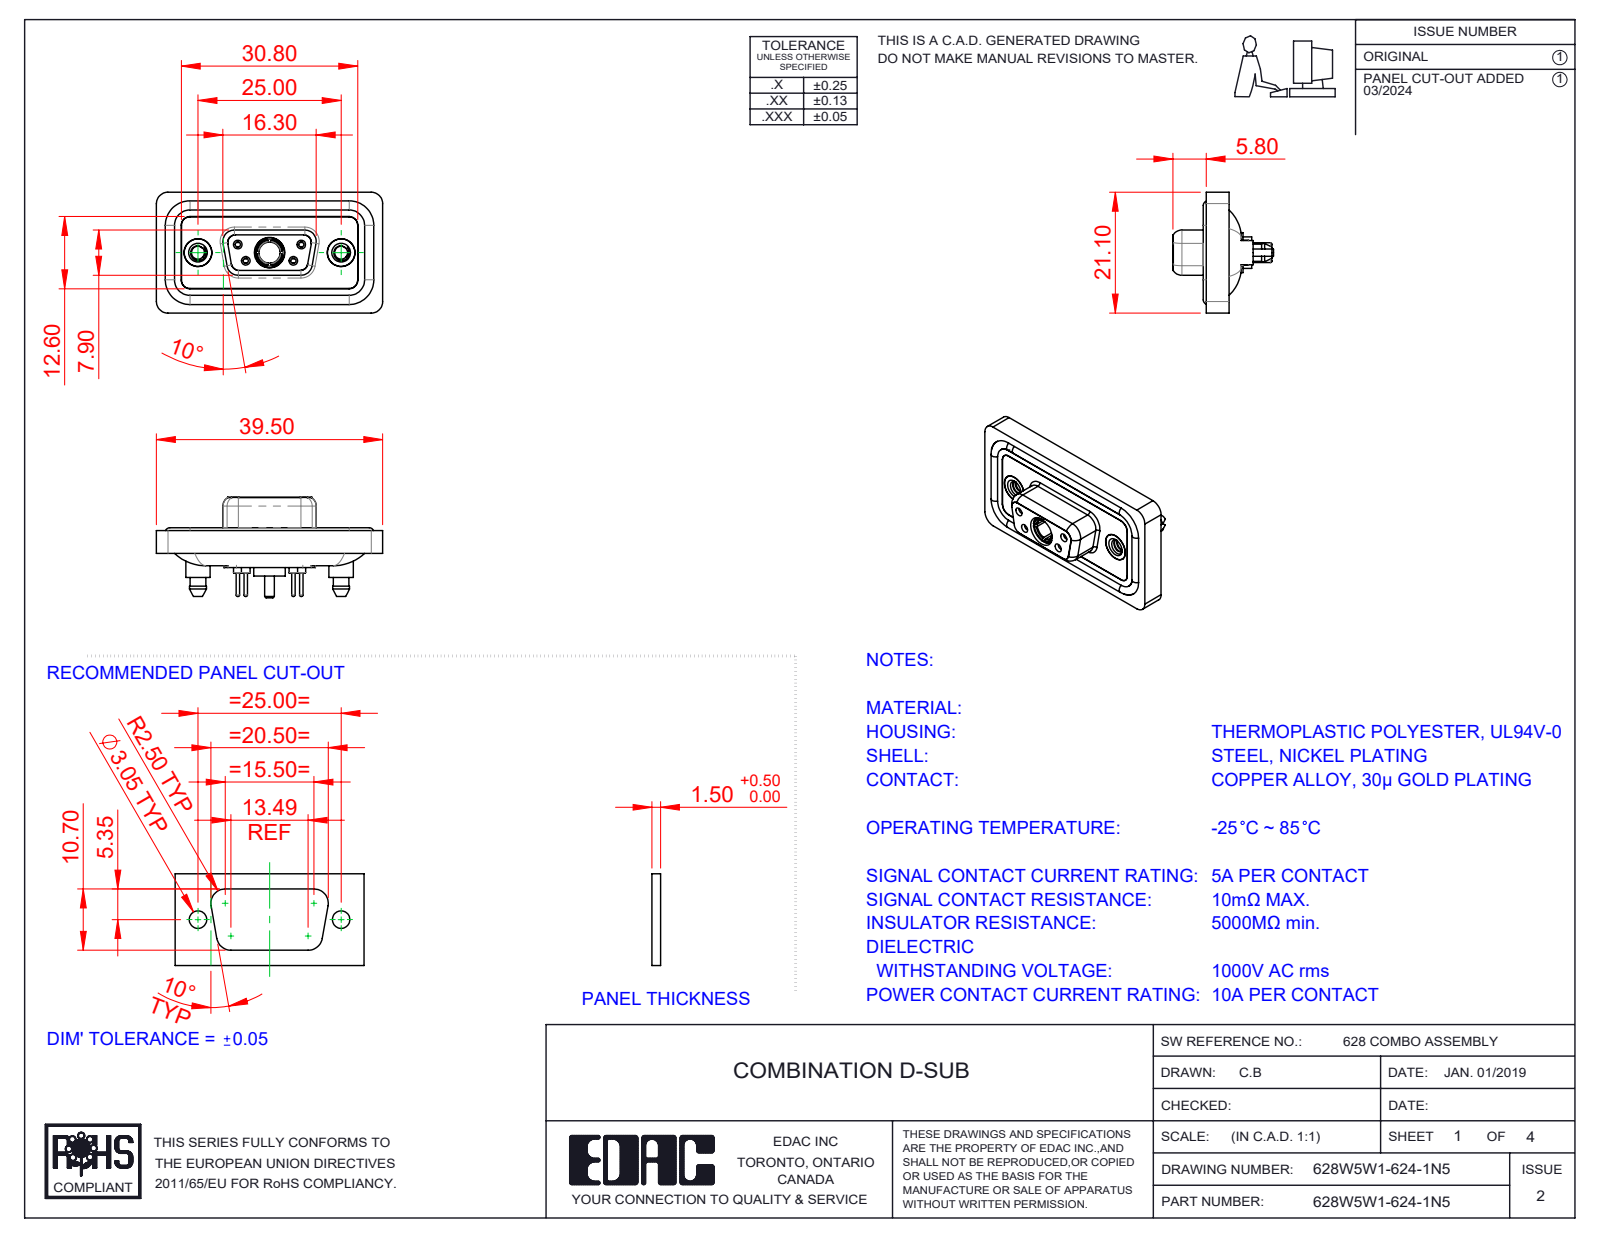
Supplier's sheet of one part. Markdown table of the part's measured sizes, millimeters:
| quantity | value |
| --- | --- |
| part name | 628Combo Threaded Boardlock_5; 628Combo Shell Front_09 Contacts; 628W5W1-624-1N5; 628Combo Shell Rear_09 Contacts (+5 more) |
| STEP written by | SolidWorks 2023 (CONFIG_CONTROL_DESIGN) |
| units | millimeters |
| bodies | 13 solids, 730 faces (210 planar, 319 cylindrical, 201 other) |
| overall size | 39.5 × 21.1 × 17.55 |
| volume | 4 886 mm³ |
| surface area | 7 956 mm² |
| round holes (diameter × count) | 0.9 × 4, 1.1 × 4, 1.5 × 4, 2 × 4, 4.85 × 3, 1.6 × 2, 1.7 × 2, 2.26 × 2, 4 × 2, 4.05 × 2, 5 × 2, 3.7 × 1 |
| round bosses / shafts (diameter × count) | 1.6 × 6, 2.2 × 4, 0.6 × 4, 5.4 × 2, 4.95 × 2, 4.8 × 2, 4.25 × 2, 5.5 × 1 |
| partial cylindrical surfaces (radius × count) | 1.5 × 24, 2 × 18, 1.6 × 10, 1.35 × 8, 0.25 × 4, 0.5 × 4, 0.6 × 4, 0.65 × 4 |
| main face-to-face distances | 0.4, 2.9, 1.8, 1.1, 1.6, 0.5, 5.65, 7.45, 5.35, 3.6 |
| hole center spacings | 3.16, 5.72, 7.1, 12.5, 18.1, 4.39, 4.4, 8.31 |
